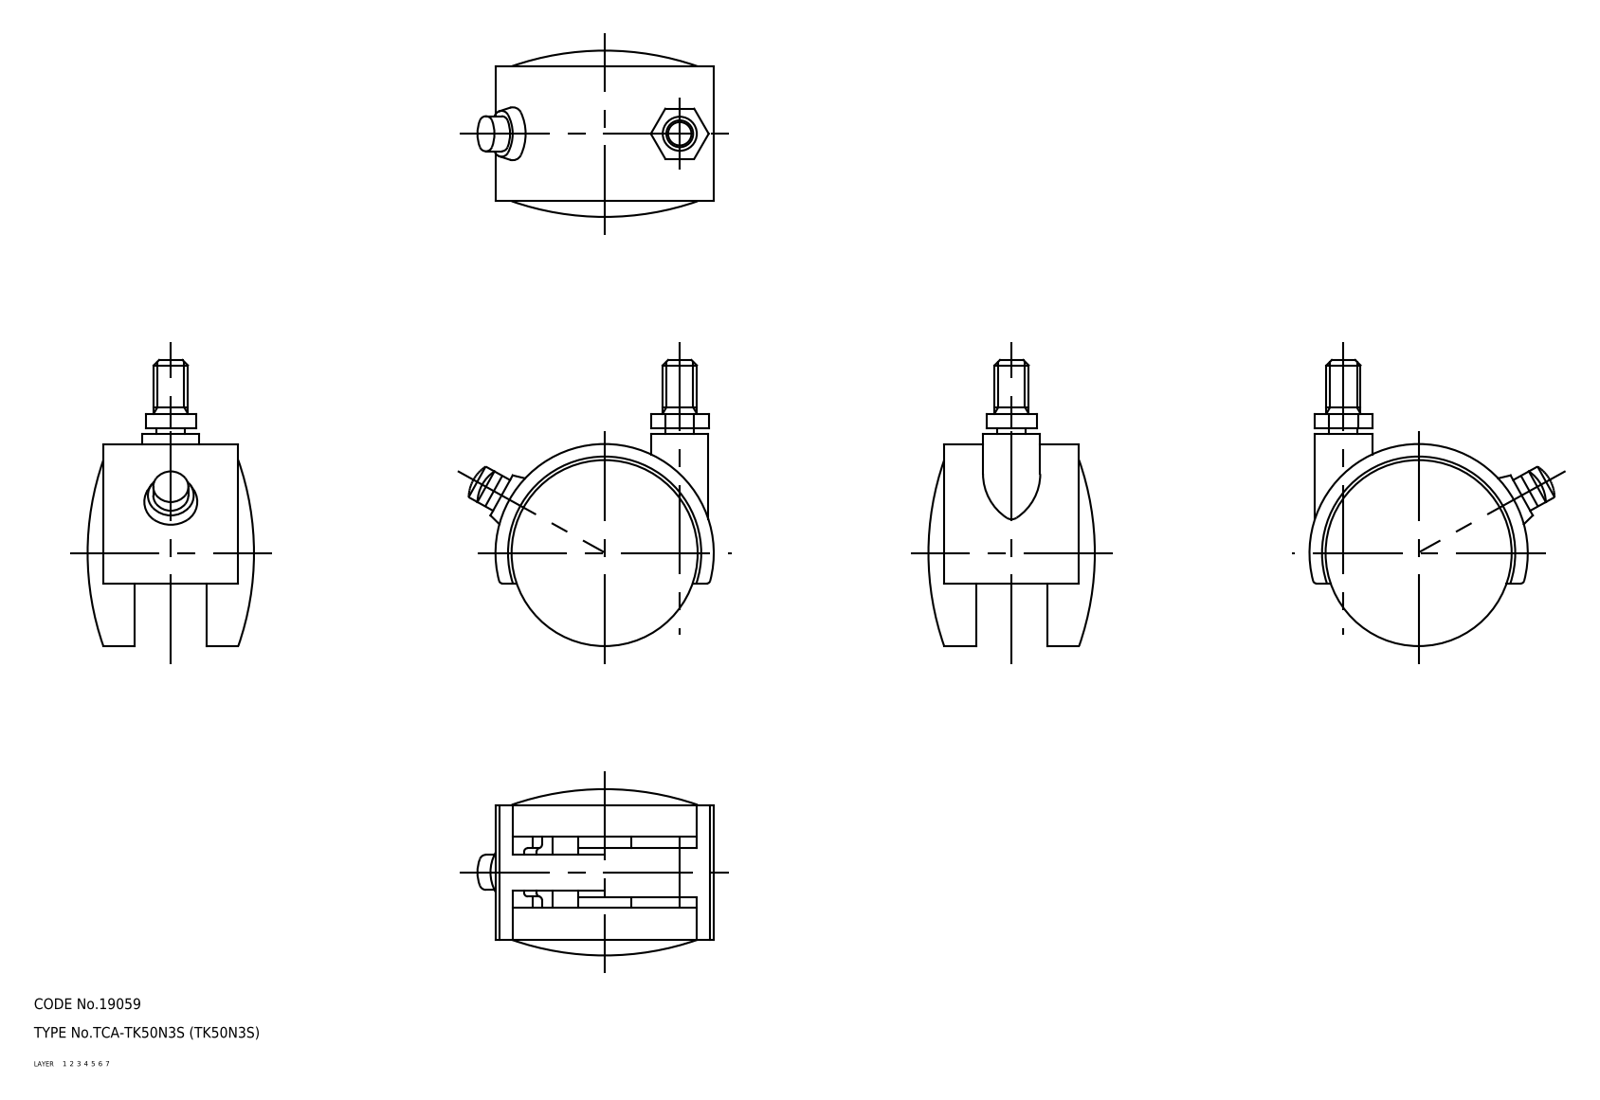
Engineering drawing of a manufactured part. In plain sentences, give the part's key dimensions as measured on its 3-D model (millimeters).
The part is named "wheel; main shaft; TK50N3S_4787_36". Its 3-D file was written by "CADfix (AUTOMOTIVE_DESIGN)". It is 4 solids with 100 faces: 0 planar, 0 cylindrical and 100 other. Overall it measures 80 by 66.05 by 46.5 millimeters. Its volume is 69 179 cubic millimeters and its surface area 30 166 square millimeters.
